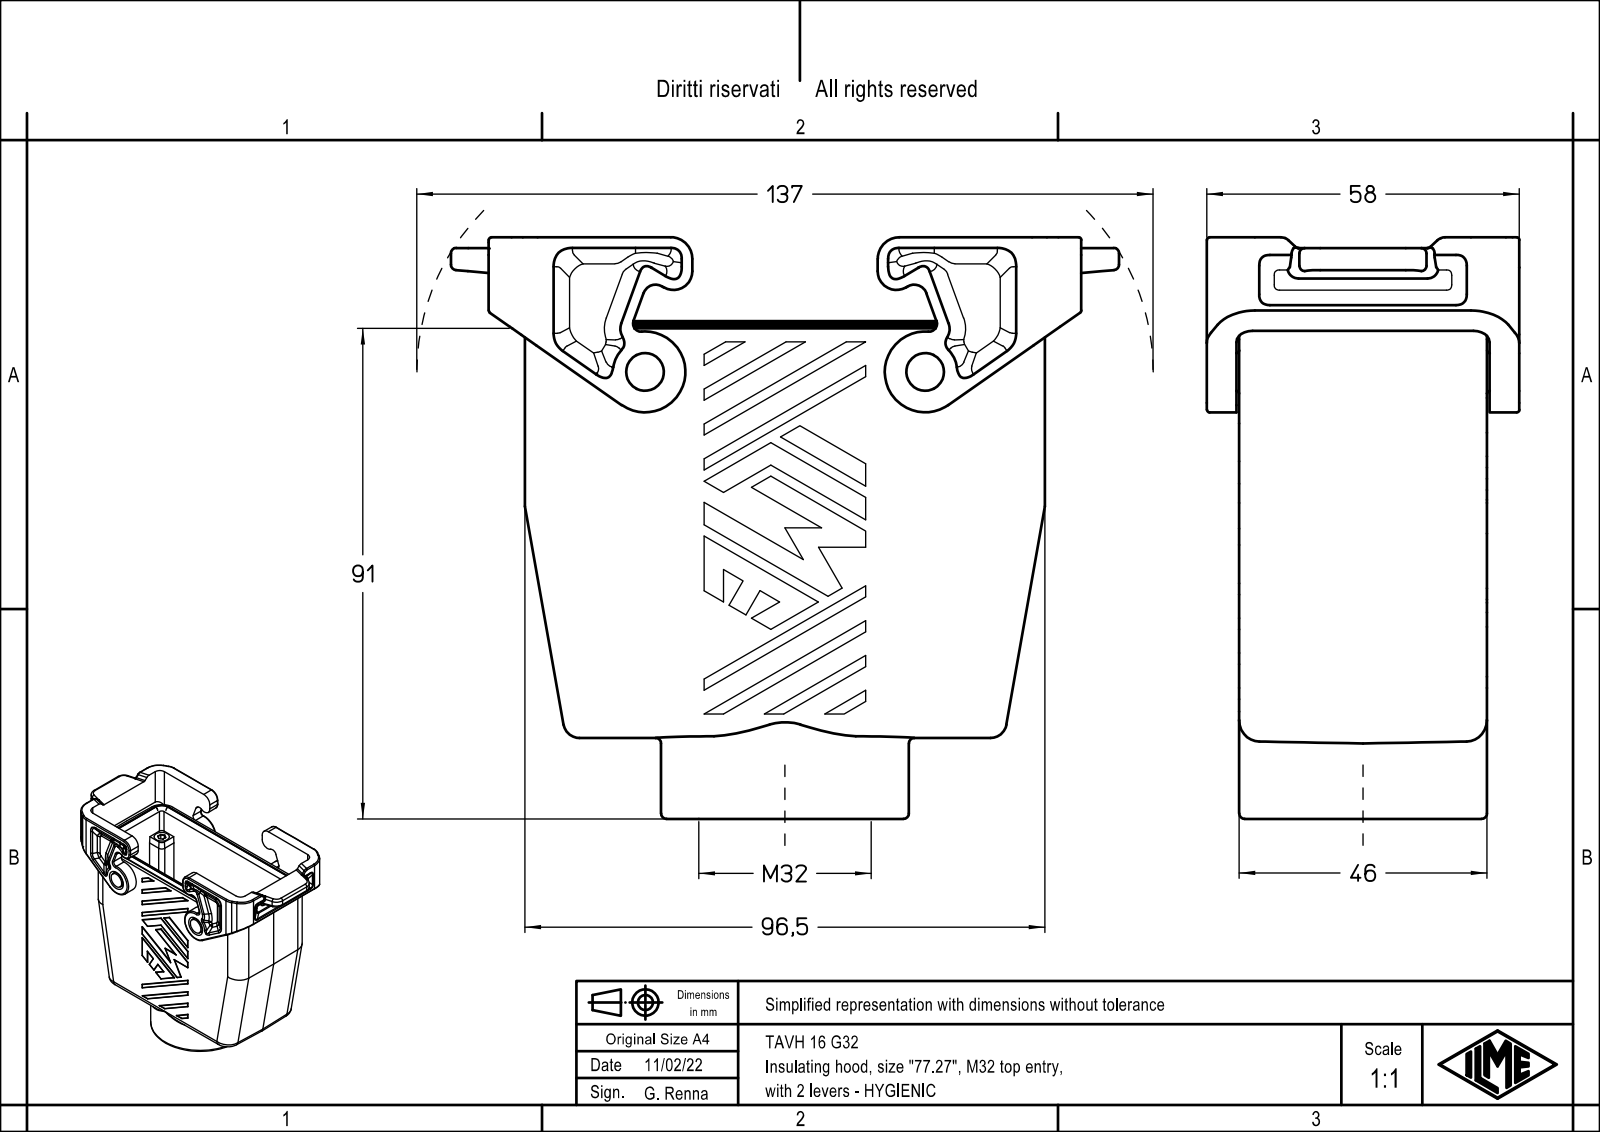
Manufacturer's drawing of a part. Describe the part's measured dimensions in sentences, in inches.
The part is named "TAVH 16 G32". Its 3-D file was written by "Creo Elements/Direct Modeling 20.1B 02-Apr-2019 (C) Parametric Technology GmbH (AUTOMOTIVE_DESIGN)". It is 1 solid with 562 faces: 218 planar, 282 cylindrical and 62 other. Overall it measures 4.882 by 4.248 by 2.283 inches. Its volume is 9.83 cubic inches and its surface area 94.23 square inches. Round holes: 1 of diameter 1.102, 1 of diameter 1.205. Round bosses or shafts: 2 of diameter 0.276, 1 of diameter 1.811. Partial cylindrical surfaces (rounded edges, fillets, slot ends): 88 of radius 0.006, 20 of radius 0.118, 16 of radius 0.039, 16 of radius 0.079, 10 of radius 0.059, 8 of radius 0.051, 8 of radius 0.236, 8 of radius 0.276. The main face-to-face distances are 0.213, 1.598, 1.386, 1.811, 0.02, 0.232, 1.618, 1.831, 0.217, 0.236.
